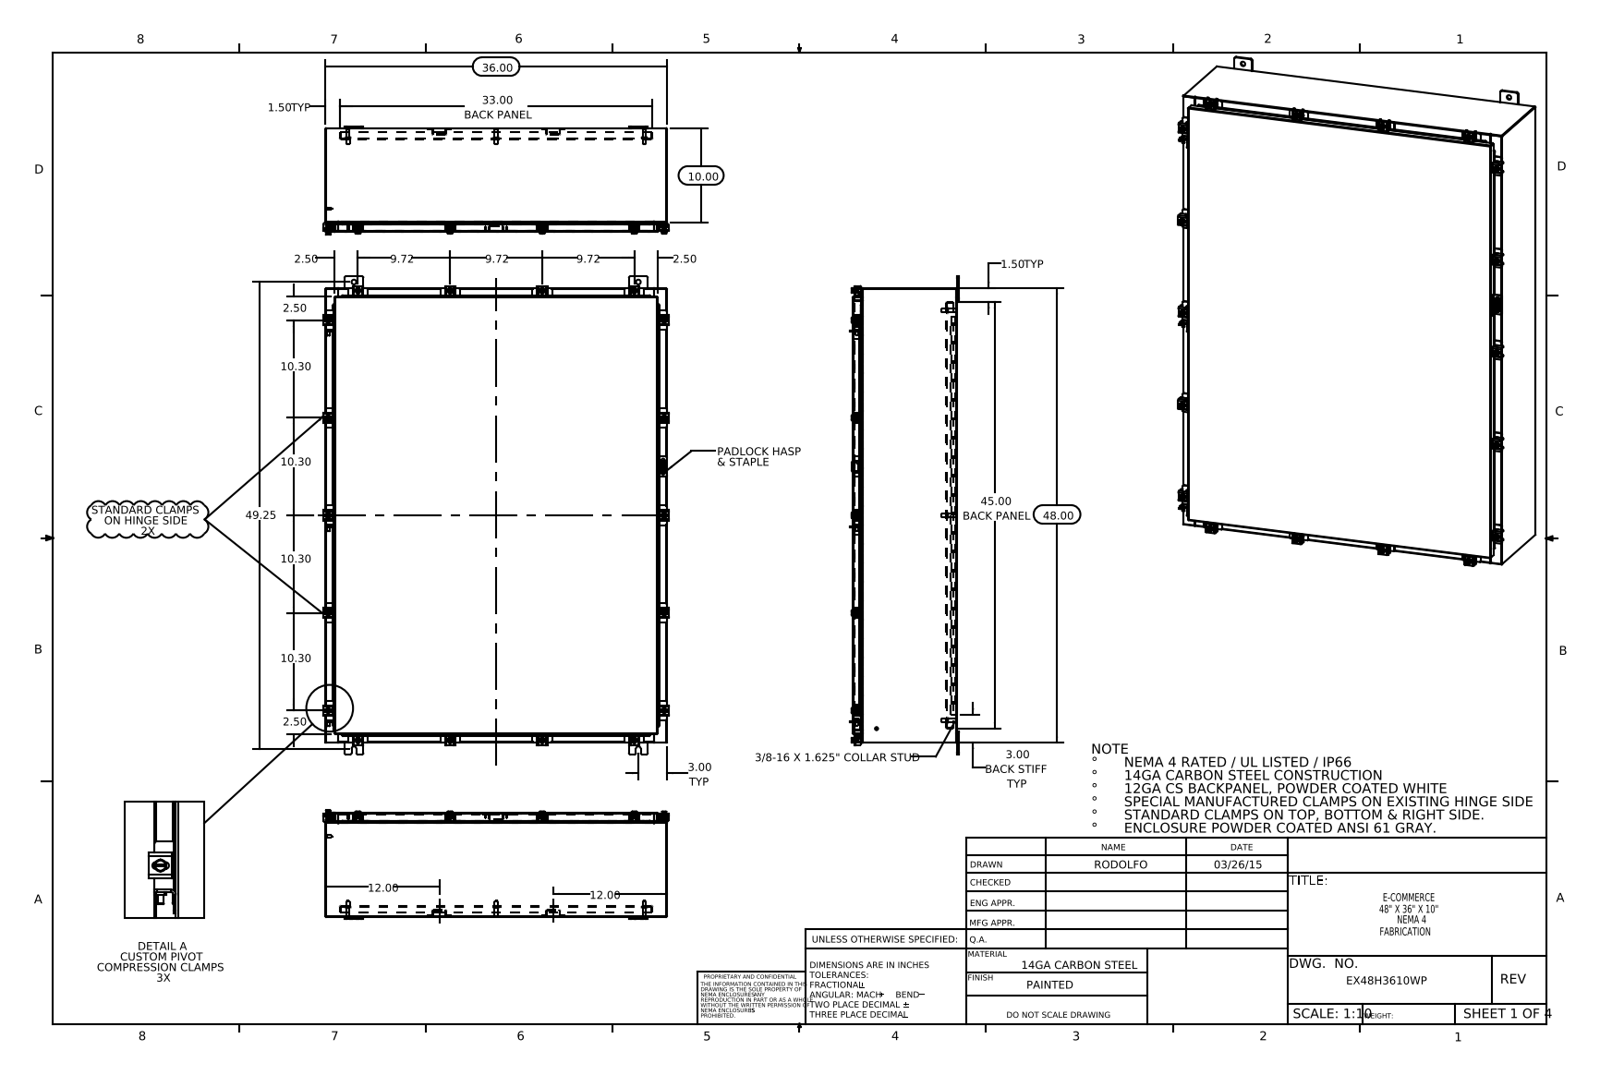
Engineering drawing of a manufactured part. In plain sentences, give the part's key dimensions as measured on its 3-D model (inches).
The part is named "EX48H3610WP Door Stiffener; N-WMT04X30402202210-00 22104005_DEFAULT; Special Clamp Assembly; EX48H3610WP Mounting Studs (+8 more)". Its 3-D file was written by "SolidWorks 2014 (CONFIG_CONTROL_DESIGN)". It is 128 solids with 3145 faces: 1631 planar, 1216 cylindrical and 298 other. Overall it measures 50.5 by 36.421 by 11.453 inches. Its volume is 623.8 cubic inches and its surface area 15 472 square inches. Round holes: 18 of diameter 0.213, 18 of diameter 0.26, 12 of diameter 0.5, 7 of diameter 0.25, 1 of diameter 0.125. Round bosses or shafts: 18 of diameter 0.5, 18 of diameter 0.25, 15 of diameter 0.399, 8 of diameter 0.625, 8 of diameter 0.375, 8 of diameter 0.33, 6 of diameter 0.157, 6 of diameter 0.14. Partial cylindrical surfaces (rounded edges, fillets, slot ends): 76 of radius 0.06, 38 of radius 0.013, 36 of radius 0.141, 34 of radius 0.088, 33 of radius 0.12, 27 of radius 0.05, 27 of radius 0.09, 26 of radius 0.145. The main face-to-face distances are 0.075, 10.9, 10.826, 10.975, 0.104, 1, 1.075, 9.826, 9.9, 1.179. The hole center spacings are 1.969, 2.347, 4.44, 13.972, 14.728, 16.126, 16.624, 17.756.
